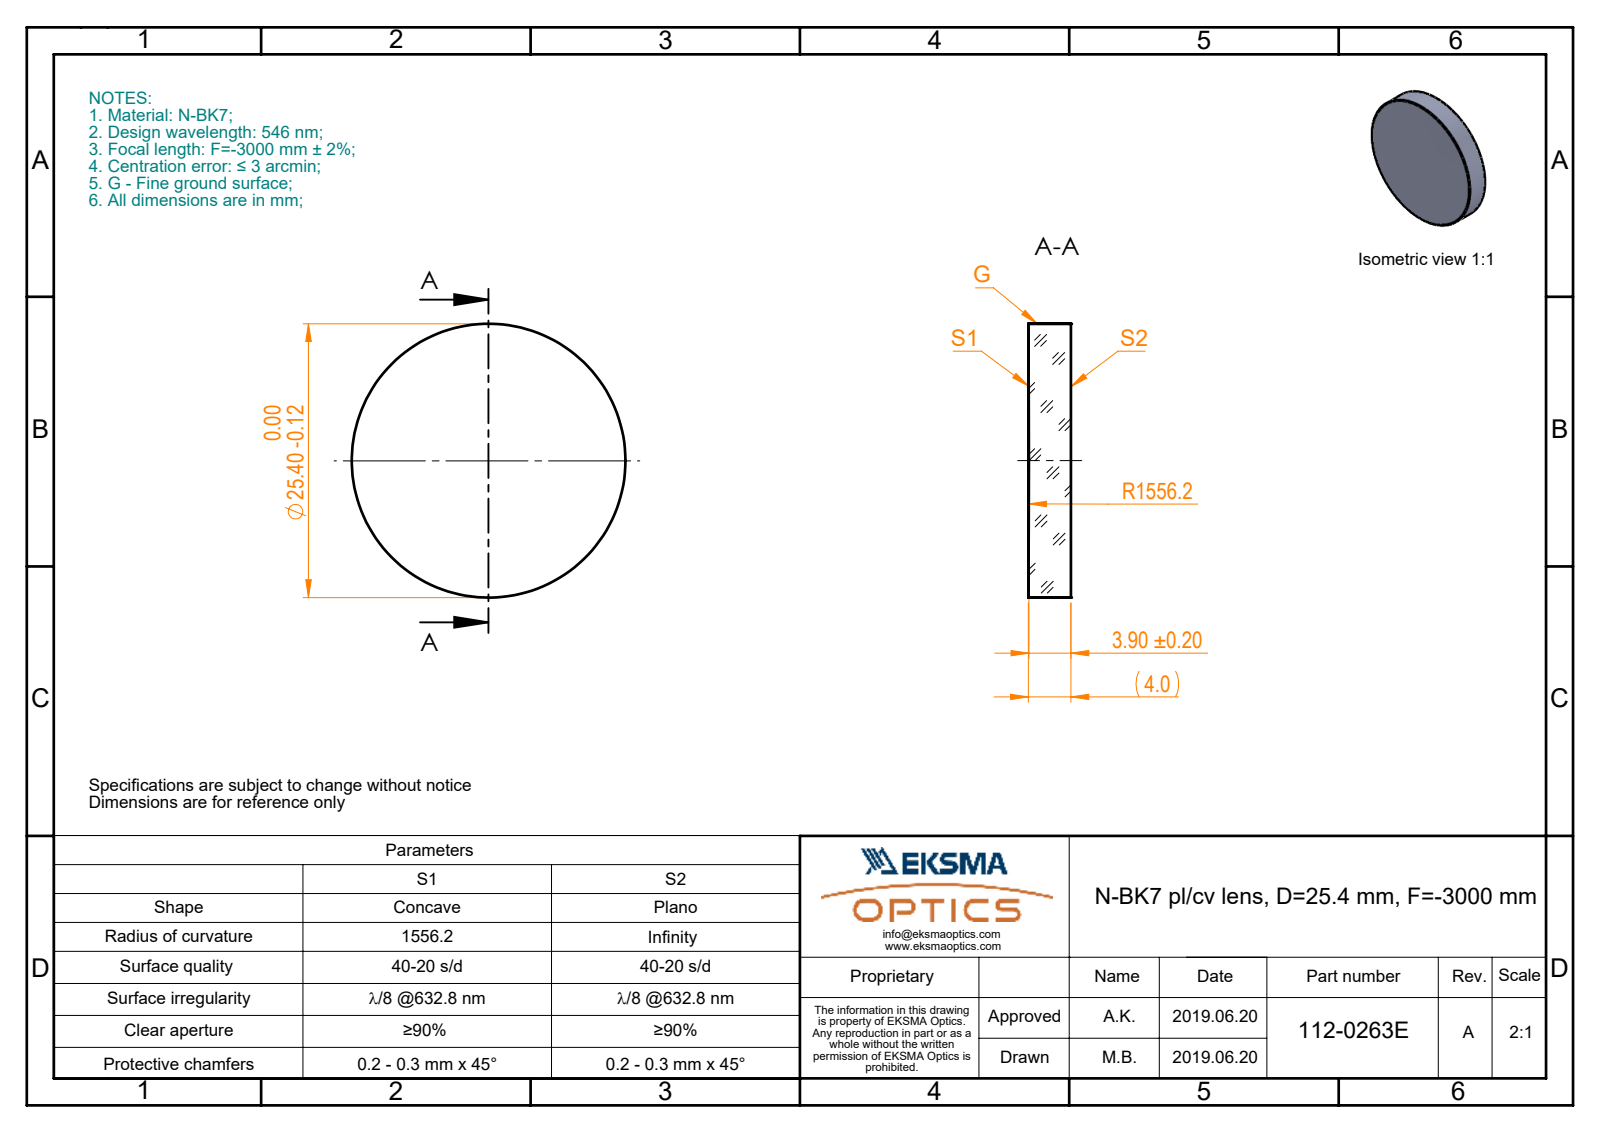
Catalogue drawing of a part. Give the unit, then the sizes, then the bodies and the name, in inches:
Units: inches
Overall size (bounding box): 1 × 1 × 0.156
Round bosses / shafts (diameter × count): ⌀1 ×1
Volume: 0.121 in³ · Surface area: 2.06 in²
Bodies: 1 solid, 5 faces (1 planar, 2 cylindrical, 2 other)
Part name (STEP PRODUCT): 112-0263E BK7 pl-cv 25.4 F-3000
STEP written by: SolidWorks 2017 (CONFIG_CONTROL_DESIGN)
